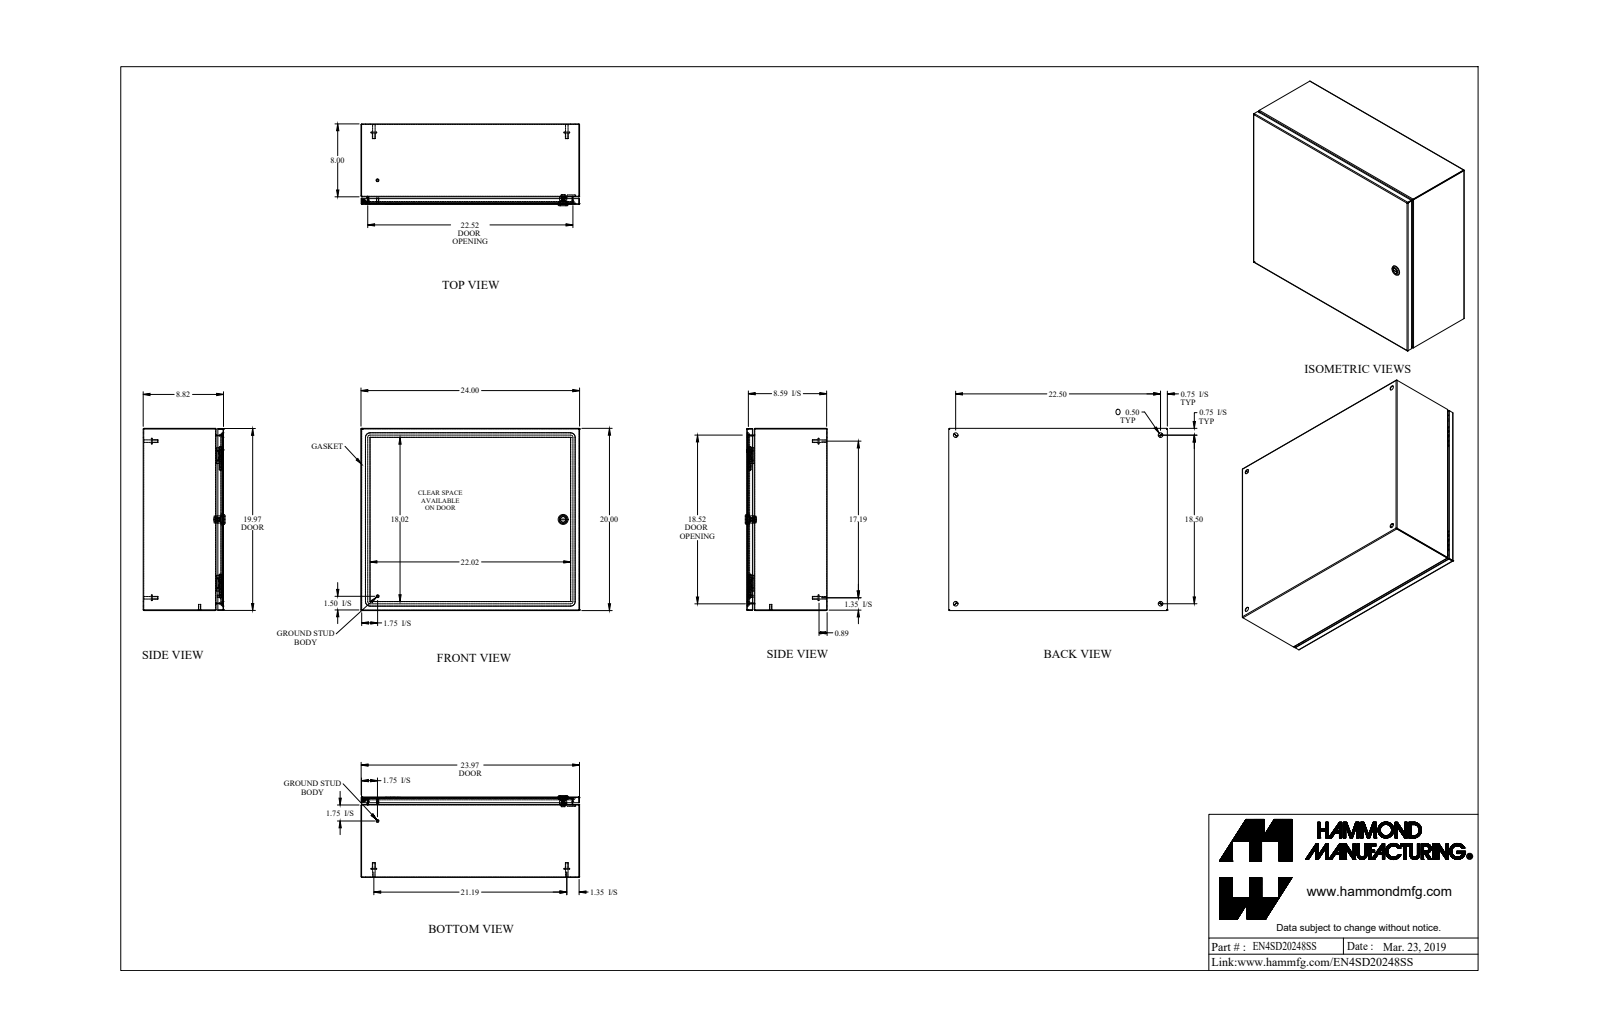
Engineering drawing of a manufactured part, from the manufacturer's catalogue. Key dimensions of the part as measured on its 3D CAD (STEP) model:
Part name (STEP PRODUCT): EN4SD20248SS_Default
STEP written by: SolidWorks 2019 (CONFIG_CONTROL_DESIGN)
Units: inches
Bodies: 22 solids, 657 faces (303 planar, 212 cylindrical, 142 other)
Overall size (bounding box): 24 × 20 × 8.982
Volume: 113.2 in³ · Surface area: 3 868 in²
Round holes (diameter × count): ⌀0.5 ×5, ⌀0.172 ×1, ⌀0.197 ×1, ⌀0.24 ×1, ⌀0.242 ×1, ⌀0.387 ×1, ⌀0.63 ×1, ⌀0.768 ×1
Round bosses / shafts (diameter × count): ⌀0.313 ×6, ⌀0.625 ×5, ⌀0.275 ×4, ⌀0.25 ×2, ⌀1.1 ×1, ⌀0.785 ×1, ⌀0.525 ×1, ⌀0.455 ×1
Partial cylindrical surfaces — rounded edges, fillets, slot ends (radius × count): R0.029 ×21, R0.086 ×21, R0.188 ×12, R0.006 ×4, R0.062 ×4, R0.25 ×4, R0.499 ×4, R0.125 ×2
Main face-to-face distances: 0.057, 8.765, 8.708, 8.822, 19.943, 23.943, 19.886, 20, 23.886, 24
Hole centre spacings: 18.5, 22.5, 23.351, 29.129, 9.31, 9.311
